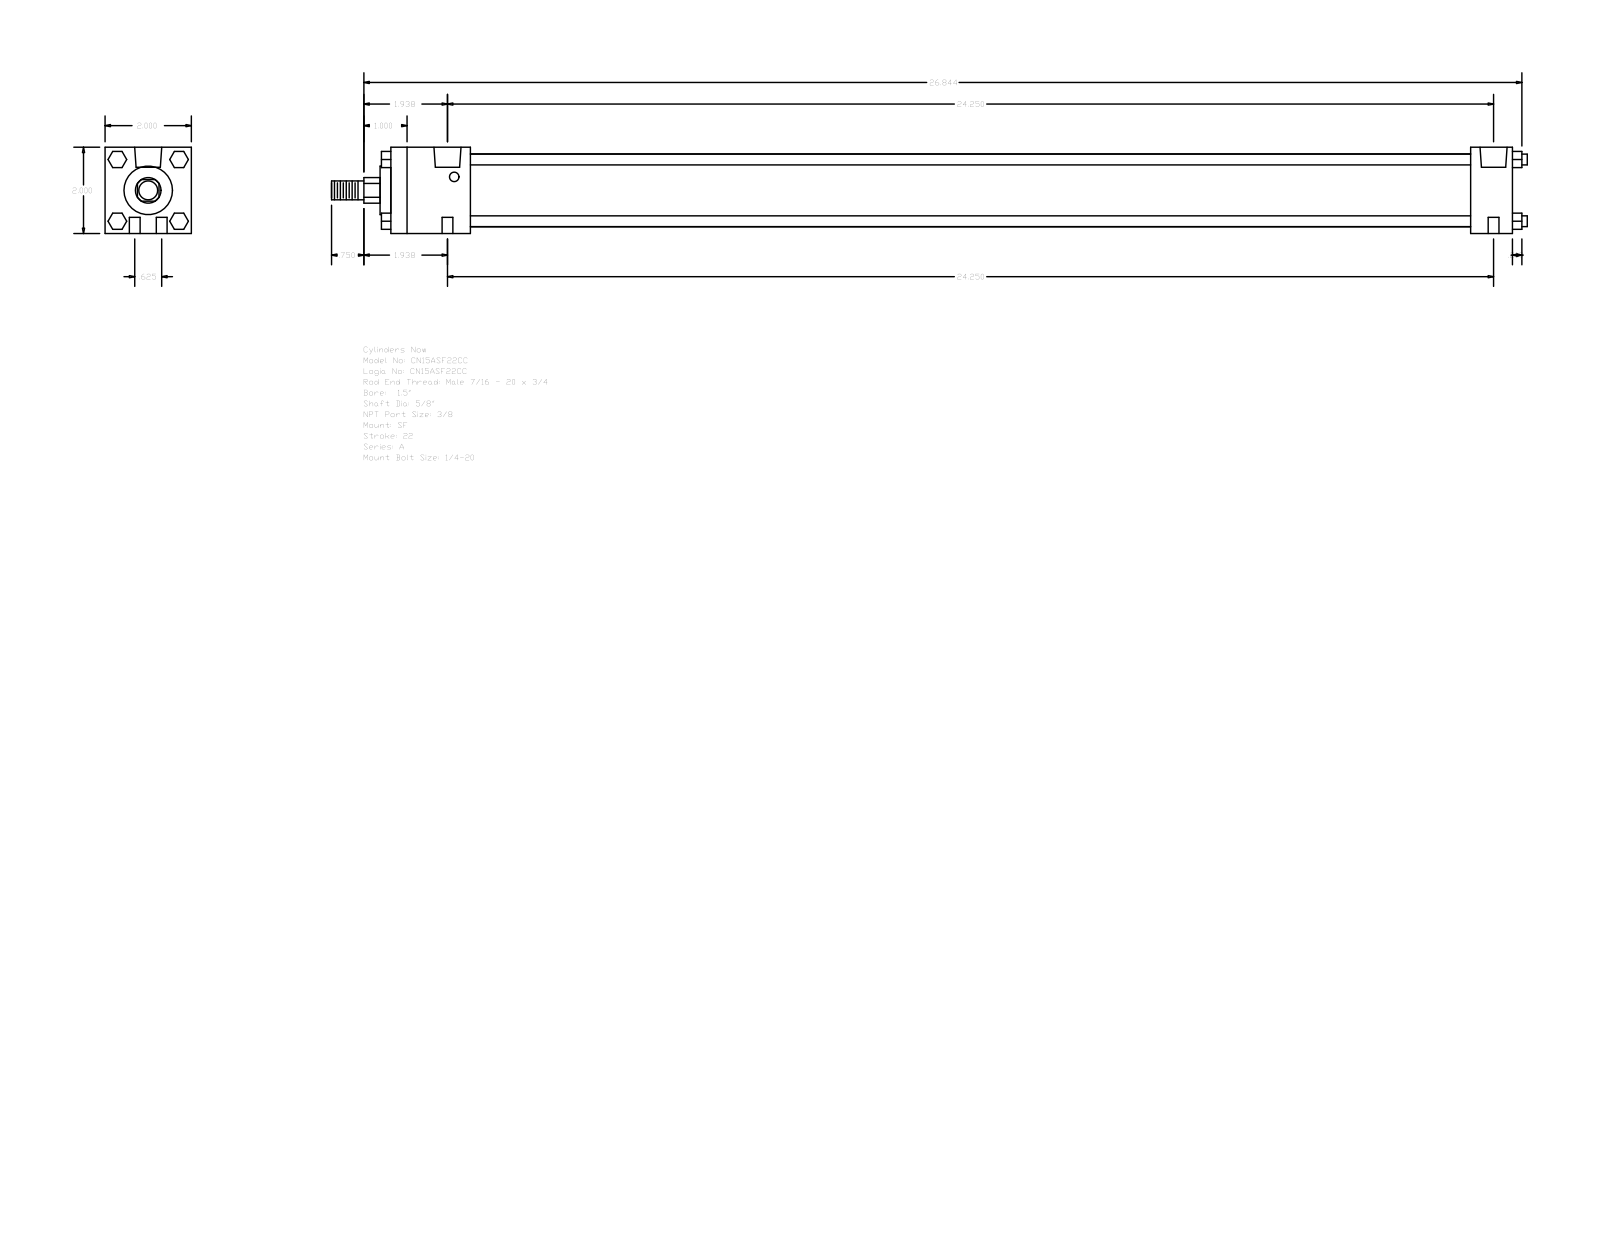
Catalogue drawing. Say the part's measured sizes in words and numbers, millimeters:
The part is named "A_SF__0150_0.625". Its 3-D file was written by "GSSL Pune (CONFIG_CONTROL_DESIGN)". It is 0 solids with 124 faces: 94 planar, 30 cylindrical and 0 other. Overall it measures 704.06 by 50.8 by 50.8 millimeters. Round holes: 4 of diameter 6.35, 2 of diameter 5.56, 2 of diameter 15.93. Round bosses or shafts: 4 of diameter 6.35, 1 of diameter 42.93, 1 of diameter 28.57, 1 of diameter 15.88, 1 of diameter 11.11. Partial cylindrical surfaces (rounded edges, fillets, slot ends): 1 of radius 7.54. The main face-to-face distances are 50.8, 660.39, 46.83, 635.79, 588.96, 613.56, 24.6, 6.35, 9.52, 53.18. The hole center spacings are 7.94, 616, 615.95, 15.88, 616.15, 608.01.
